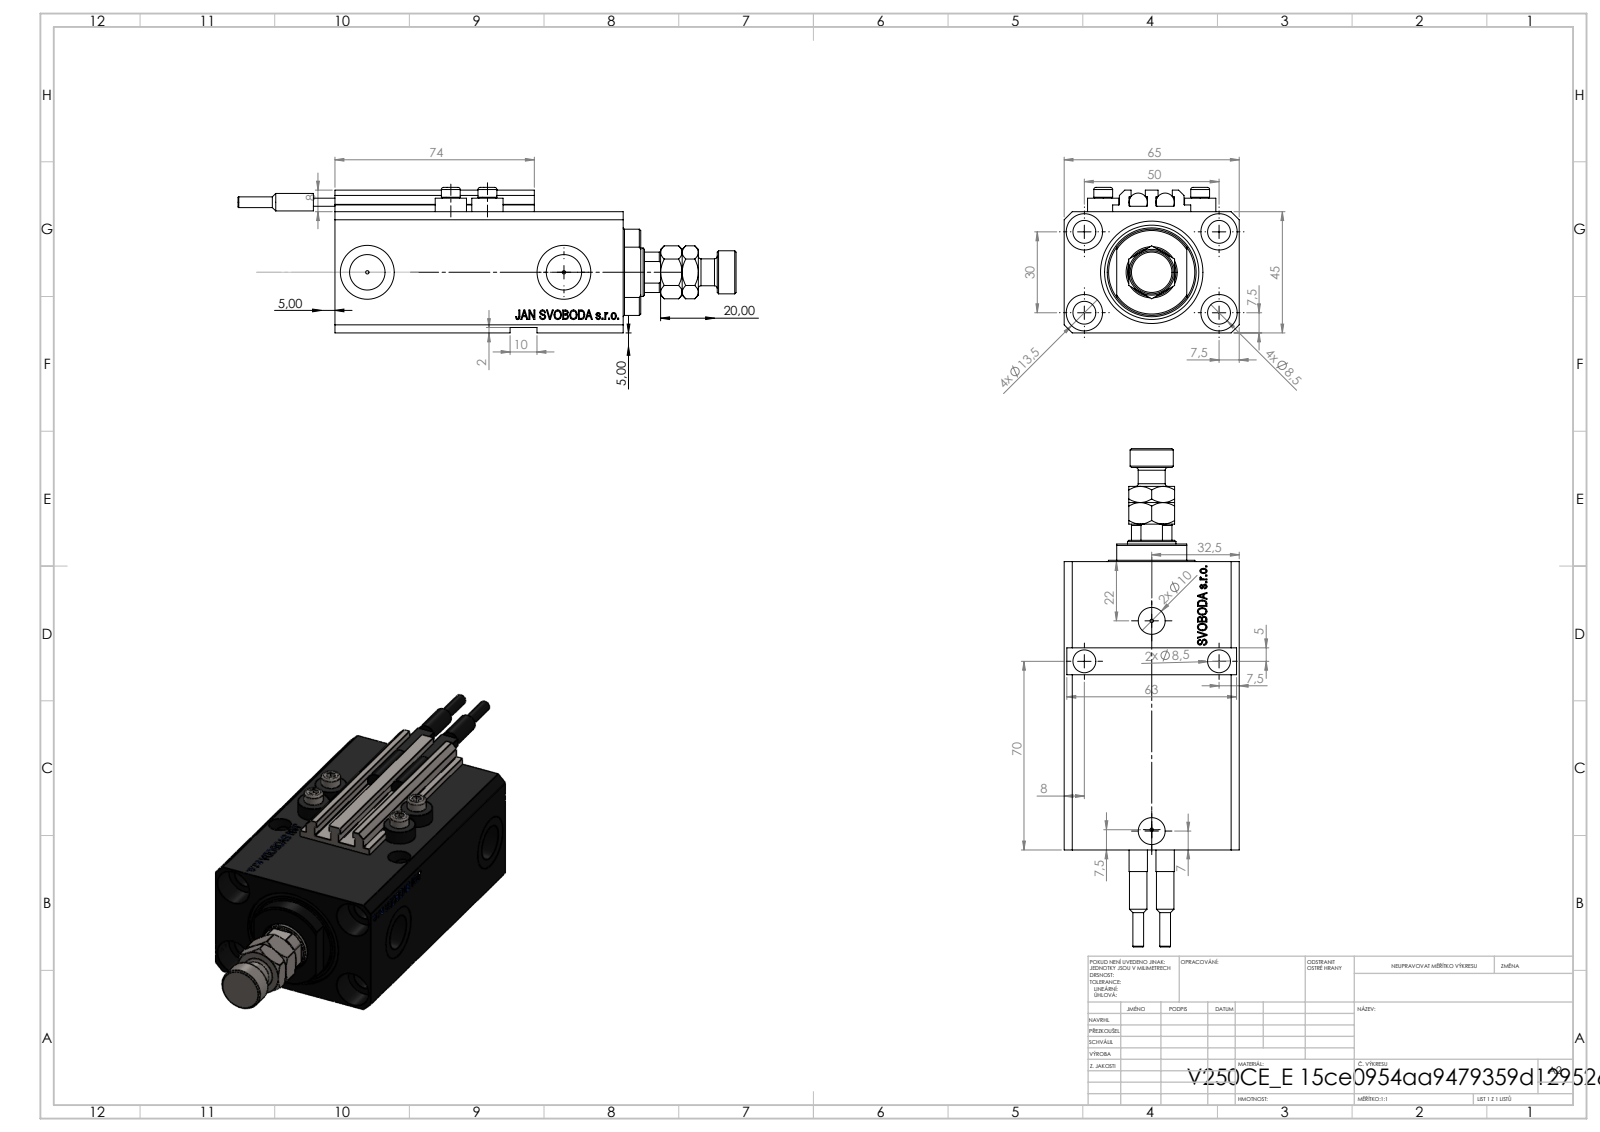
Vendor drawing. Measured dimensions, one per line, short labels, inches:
name: SWITCH_V250CE; MFA; V250CE_VC_E; V250CE_E_Body (+2 more)
written by: SolidWorks 2019 (CONFIG_CONTROL_DESIGN)
unit: in
bodies: 11 solids, 1207 faces (563 planar, 174 cylindrical, 470 other)
size: 7.283 × 2.559 × 2.126
volume: 17.01 in³; area: 128.4 in²
holes: 9× ⌀0.335, 4× ⌀0.049, 4× ⌀0.157, 4× ⌀0.531, 2× ⌀0.394, 2× ⌀0.518, 2× ⌀0.787, 1× ⌀0.709, 1× ⌀0.984, 1× ⌀1.496
bosses: 4× ⌀0.457, 4× ⌀0.276, 2× ⌀0.268, 2× ⌀0.256, 2× ⌀0.157, 1× ⌀0.63, 1× ⌀0.394
rounds: 10× R0.008, 1× R0.335, 1× R0.63
face distances: 1.772, 2.559, 0.551, 0.079, 1.85, 3.661, 0.118, 4.213, 0.945, 0.272
hole spacings: 1.148, 1.969, 0.535, 0.581, 0.595, 1.083, 1.098, 1.181
